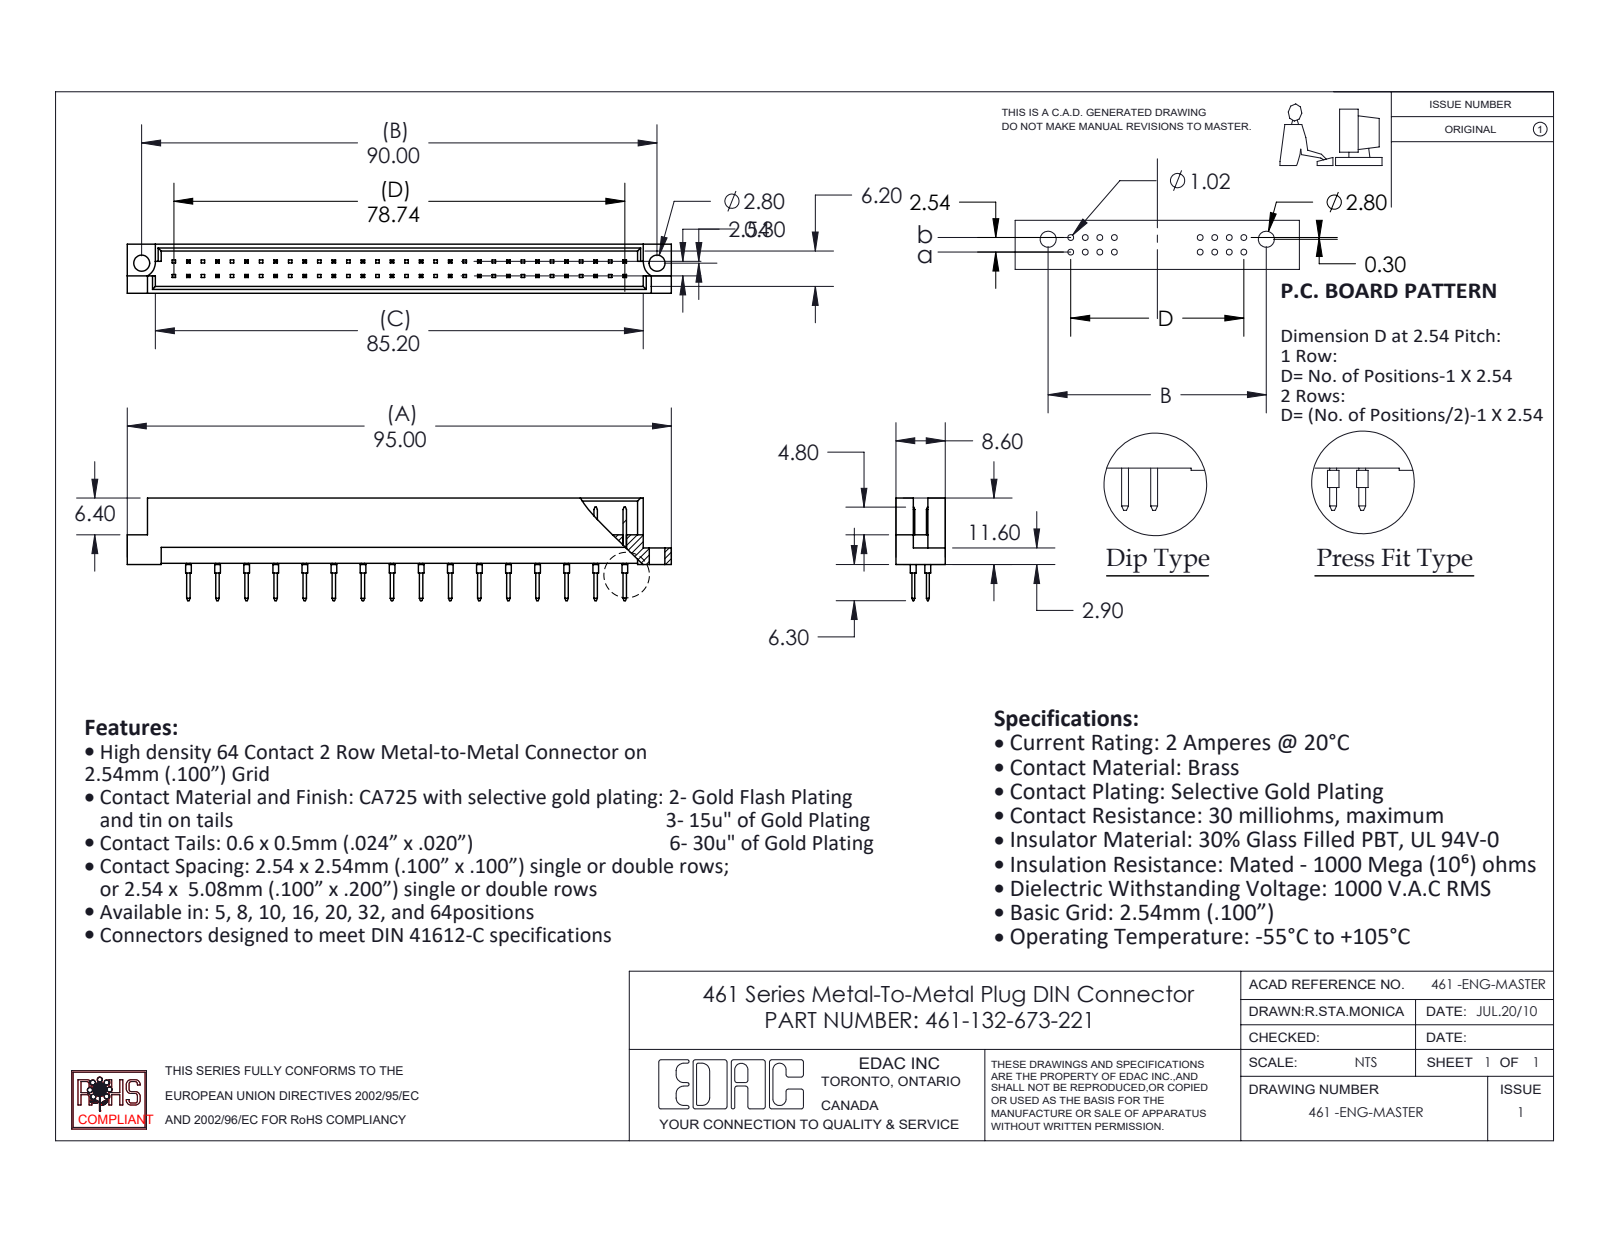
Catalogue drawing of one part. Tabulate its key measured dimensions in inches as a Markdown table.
| quantity | value |
| --- | --- |
| part name | 461 Part_64; 461-290_73; 461-132-673-221 |
| STEP written by | SolidWorks 2020 (CONFIG_CONTROL_DESIGN) |
| units | inches |
| bodies | 33 solids, 1009 faces (938 planar, 71 cylindrical, 0 other) |
| overall size | 3.74 × 0.705 × 0.339 |
| volume | 0.295 in³ |
| surface area | 10.67 in² |
| round holes (diameter × count) | 0.11 × 2 |
| round bosses / shafts (diameter × count) | 0.039 × 32 |
| partial cylindrical surfaces (radius × count) | 0.11 × 2 |
| main face-to-face distances | 0.047, 0.291, 0.339, 0.244, 0.197, 0.1, 0.129, 0.209, 0.082, 0.162 |
| hole center spacings | 3.543 |
